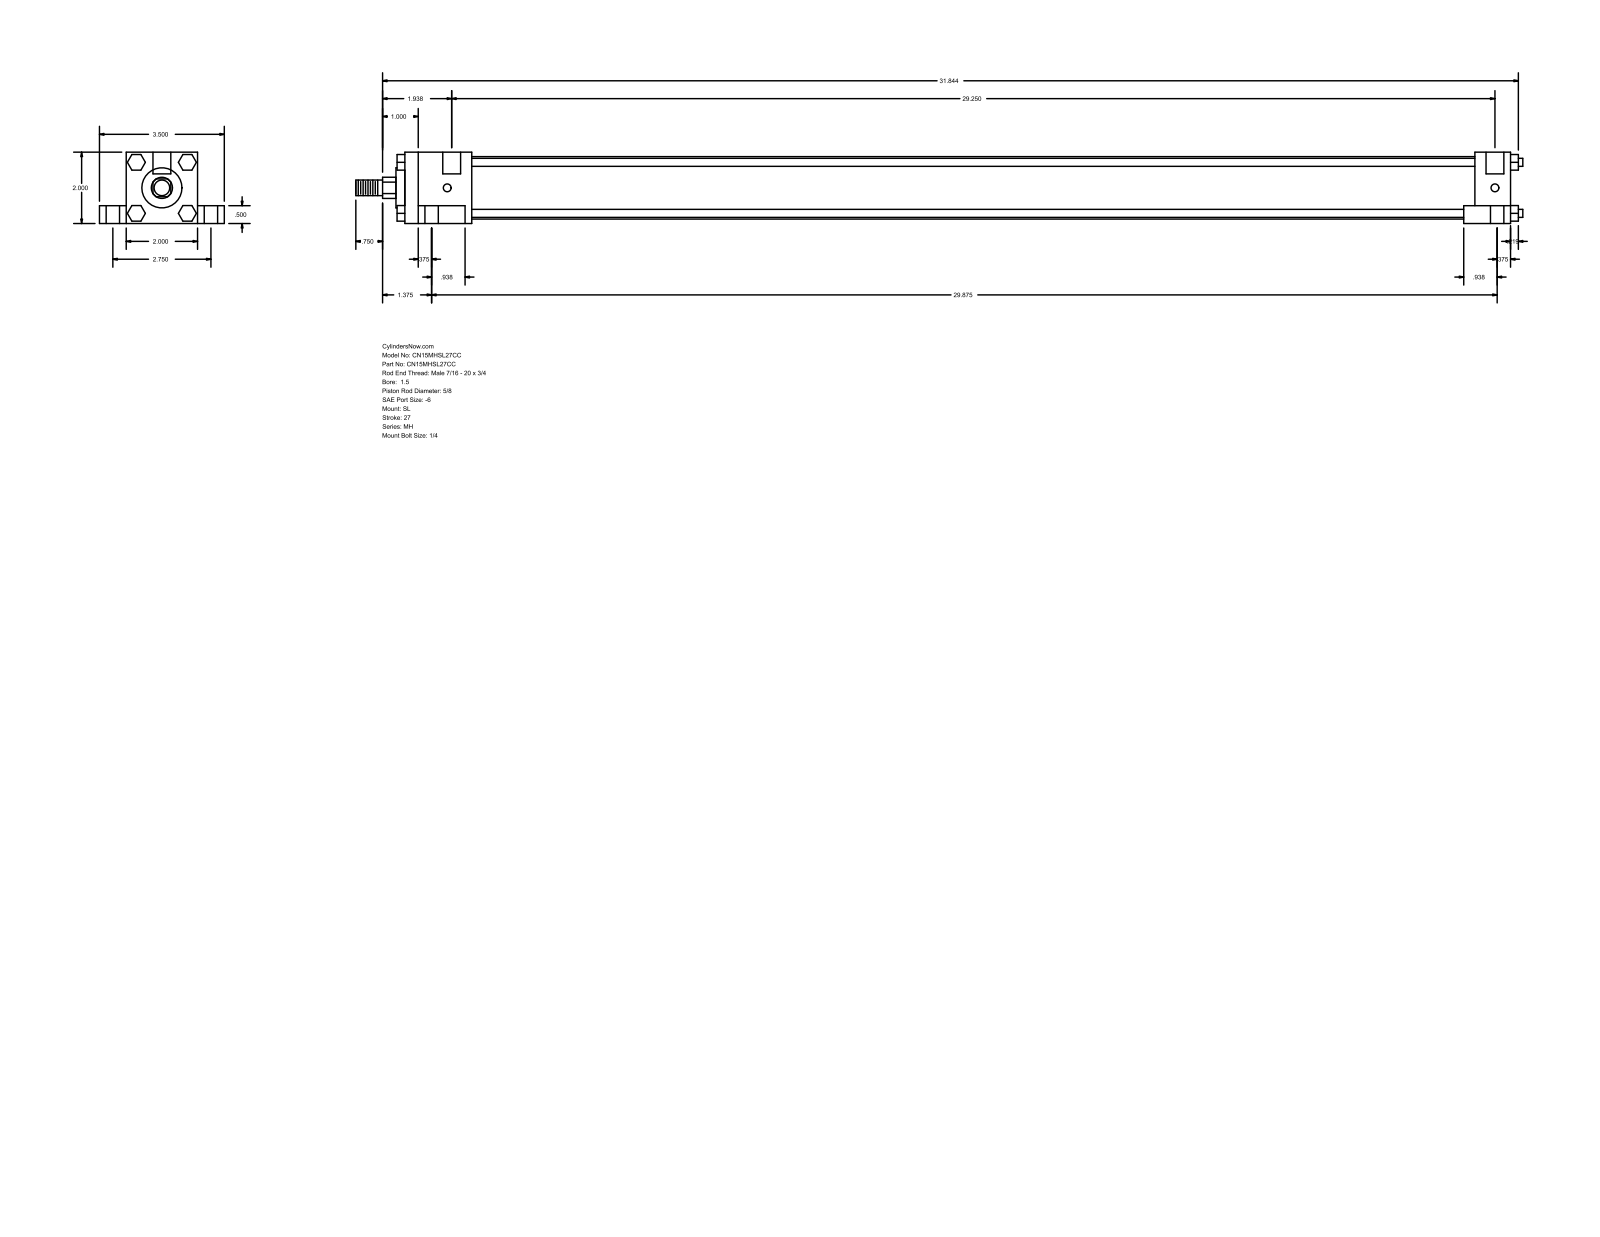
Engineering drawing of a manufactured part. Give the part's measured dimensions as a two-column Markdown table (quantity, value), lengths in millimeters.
| quantity | value |
| --- | --- |
| part name | MH_SL__0150_0.625 |
| STEP written by | GSSL Pune (CONFIG_CONTROL_DESIGN) |
| units | millimeters |
| bodies | 0 solids, 148 faces (112 planar, 36 cylindrical, 0 other) |
| overall size | 831.06 × 88.9 × 50.8 |
| round holes (diameter × count) | 5.56 × 4, 9.53 × 4, 15.88 × 4, 12.7 × 2 |
| round bosses / shafts (diameter × count) | 5.71 × 4, 44.45 × 1, 28.57 × 1, 15.88 × 1, 11.11 × 1 |
| partial cylindrical surfaces (radius × count) | 7.54 × 1 |
| main face-to-face distances | 50.8, 38.1, 19.05, 12.7, 69.85, 787.39, 9.52, 762, 25.39, 47.62 |
| hole center spacings | 34.96, 36.65, 37.73, 69.84, 745.36, 746.12, 748.52, 758.04 |
